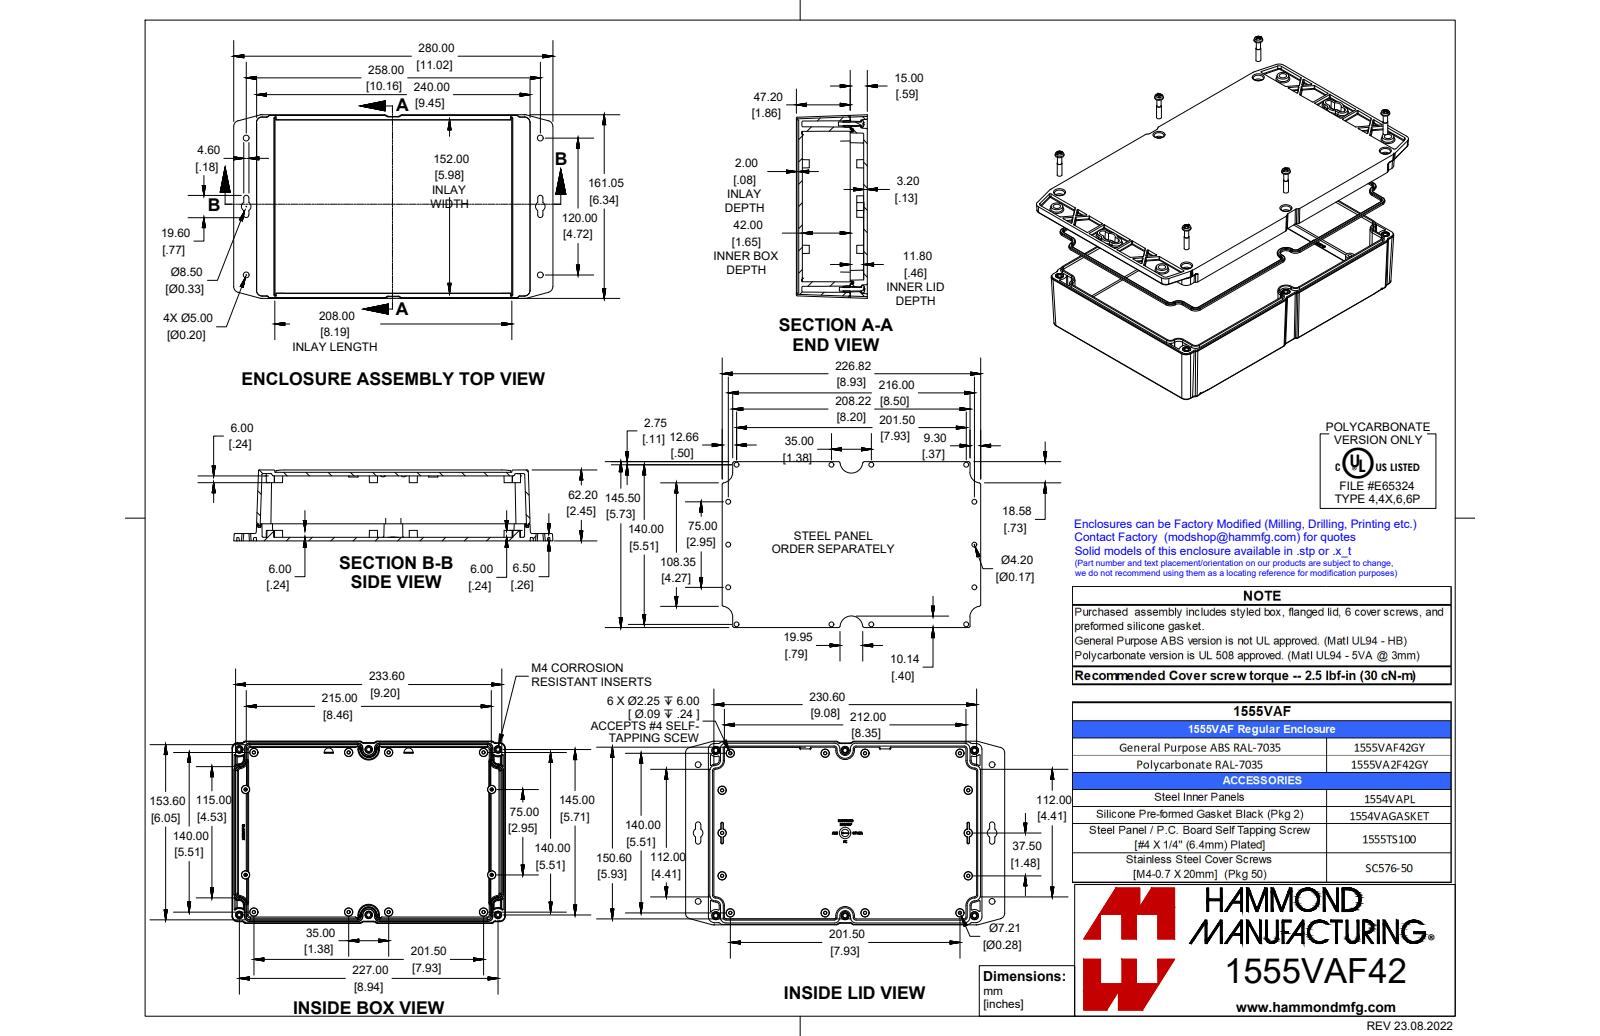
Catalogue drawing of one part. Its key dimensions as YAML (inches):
part_name: "1555VA2F42GY"
step_written_by: "SolidWorks 2021 (AUTOMOTIVE_DESIGN)"
units: inches
bodies: {solids: 9, faces: 1874, planar: 610, cylindrical: 436, other: 828}
overall_size: [11.024, 6.34, 2.449]
volume: 27.71
surface_area: 452
round_holes:
  - {diameter: 0.128, count: 6}
  - {diameter: 0.158, count: 6}
round_bosses_or_shafts:
  - {diameter: 0.276, count: 6}
  - {diameter: 0.153, count: 6}
  - {diameter: 0.138, count: 6}
partial_cylinders:
  - {radius: 0.02, count: 130}
  - {radius: 0.031, count: 43}
  - {radius: 0.012, count: 22}
  - {radius: 0.079, count: 16}
  - {radius: 0.039, count: 14}
  - {radius: 0.1, count: 12}
  - {radius: 0.195, count: 12}
  - {radius: 0.024, count: 8}
face_to_face_distances: [0.126, 2.244, 2.37, 2.118, 0.079, 0.118, 0.256, 2.323, 0.472, 0.047]
hole_center_spacings: [4.469, 7.25, 5.709, 8.937, 10.605]
